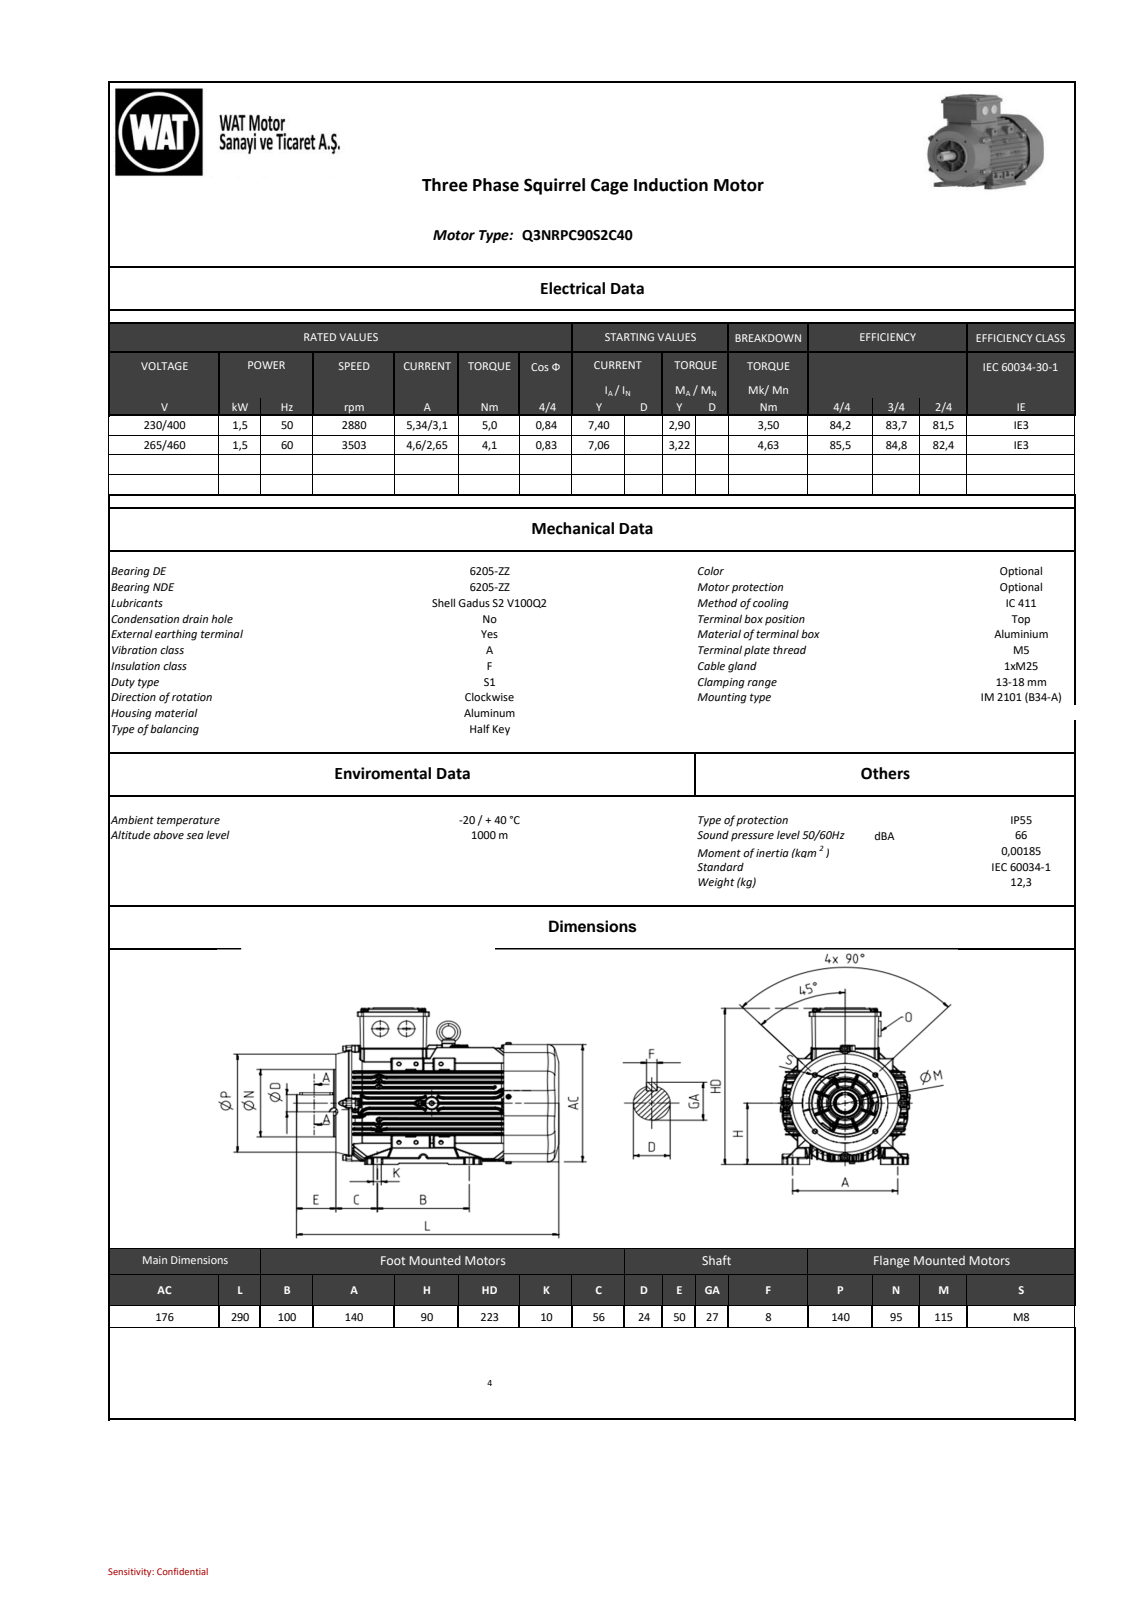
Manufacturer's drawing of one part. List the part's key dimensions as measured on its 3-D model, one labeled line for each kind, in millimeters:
Part name (STEP PRODUCT): C90137A8C608yd4i
STEP written by: SIEMENS PLM Software NX 11.0 (AUTOMOTIVE_DESIGN)
Units: millimetres
Bodies: 0 solids, 14640 faces (3462 planar, 4337 cylindrical, 6841 other)
Overall size (bounding box): 290 × 211.5 × 180
Round holes (diameter × count): ⌀4.2 ×6, ⌀9 ×6, ⌀5.1 ×5, ⌀6.8 ×4, ⌀12 ×4, ⌀2 ×2, ⌀2.5 ×2, ⌀3 ×2, ⌀7 ×2, ⌀4 ×1, ⌀8 ×1, ⌀12.2 ×1
Round bosses / shafts (diameter × count): ⌀5 ×12, ⌀8 ×8, ⌀4 ×8, ⌀9.4 ×6, ⌀8.5 ×6, ⌀9.2 ×5, ⌀25 ×3, ⌀35 ×2
Partial cylindrical surfaces — rounded edges, fillets, slot ends (radius × count): R0.5 ×1146, R1 ×711, R0.8 ×511, R0.2 ×144, R0.3 ×120, R1.5 ×98, R4 ×88, R2 ×85
Main face-to-face distances: 0.8, 5.51, 56, 39, 2, 5.5, 28, 5.81, 4.94, 5.54
Hole centre spacings: 20, 81, 14.14, 14.15, 28.28, 57.28, 57.5, 81.32
